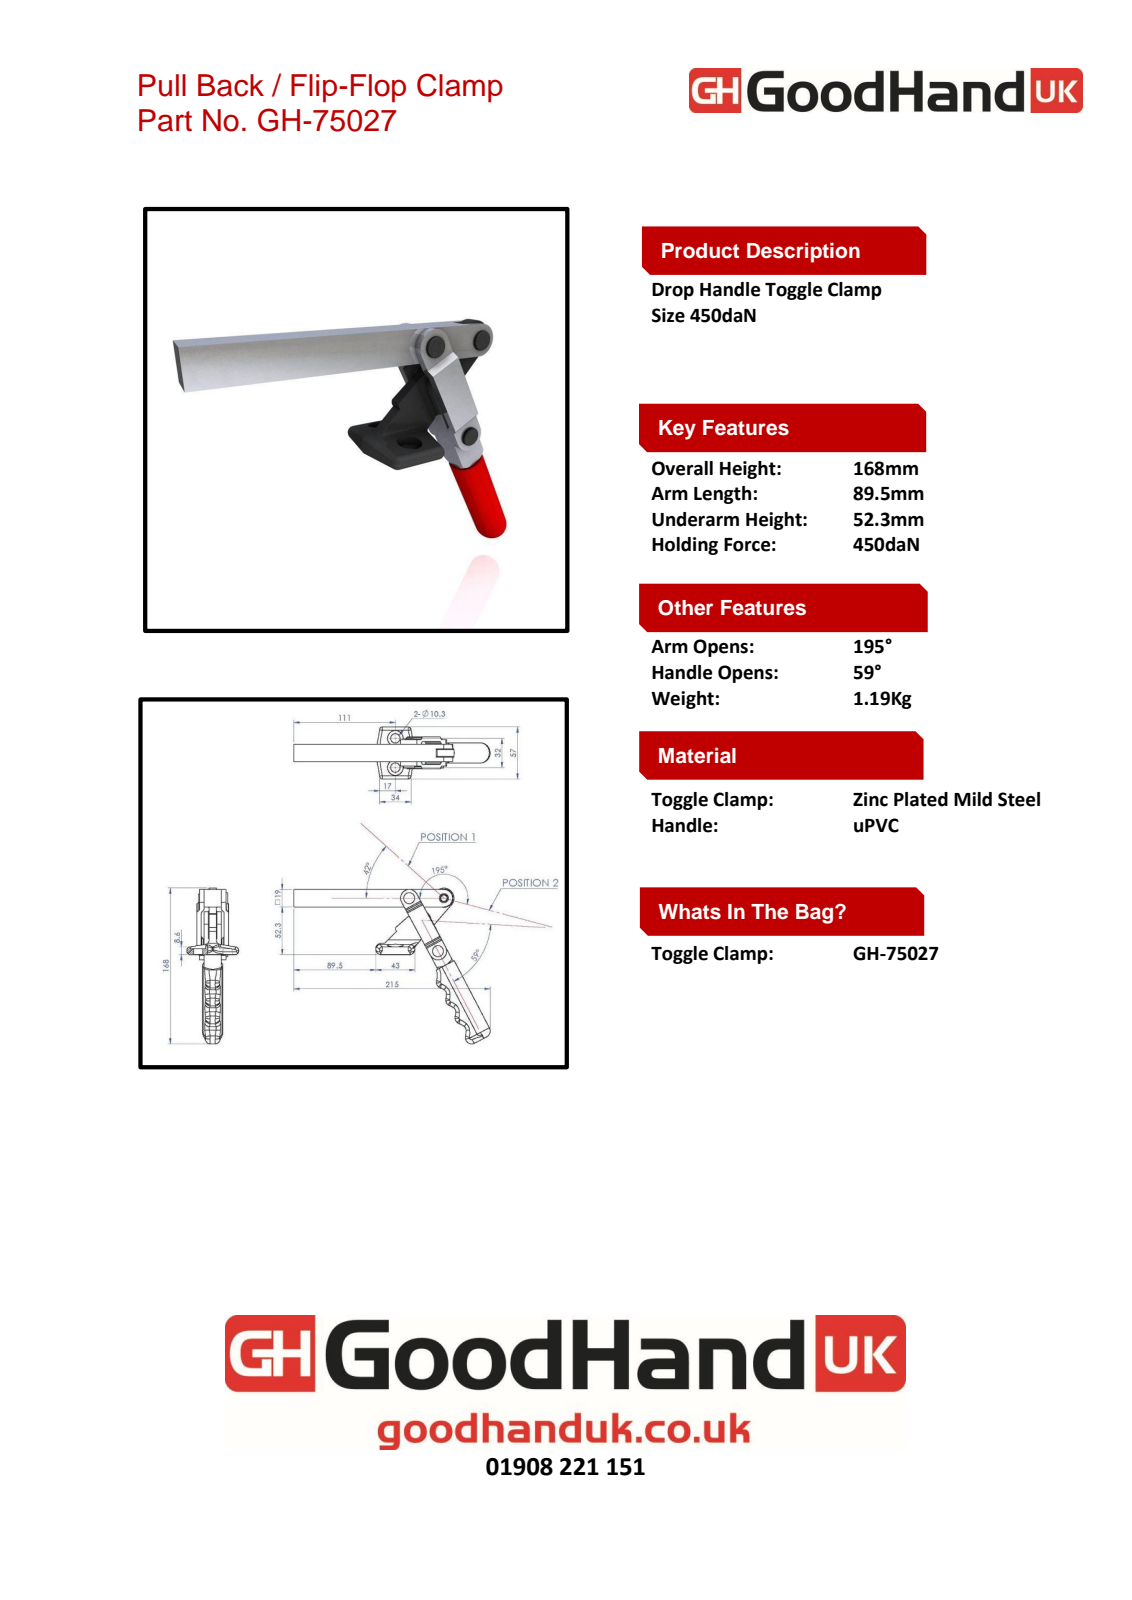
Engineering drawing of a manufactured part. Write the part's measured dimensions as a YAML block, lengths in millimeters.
part_name: "Group3^GH-75027(簡化); GH-75027(簡化); Group2^GH-75027(簡化); 27502713-2^GH-75027(簡化) (+1 more)"
step_written_by: "SolidWorks 2016 (AUTOMOTIVE_DESIGN)"
units: millimeters
bodies: {solids: 4, faces: 265, planar: 72, cylindrical: 116, other: 77}
overall_size: [214.63, 170.5, 57]
volume: 166800
surface_area: 48815
round_holes:
  - {diameter: 6, count: 4}
  - {diameter: 10.3, count: 2}
  - {diameter: 17.1, count: 2}
round_bosses_or_shafts:
  - {diameter: 20, count: 2}
  - {diameter: 10, count: 2}
  - {diameter: 7, count: 2}
partial_cylinders:
  - {radius: 2, count: 16}
  - {radius: 3, count: 12}
  - {radius: 20, count: 7}
  - {radius: 5, count: 6}
  - {radius: 7, count: 4}
  - {radius: 9.5, count: 4}
  - {radius: 0.5, count: 3}
  - {radius: 4.31, count: 2}
face_to_face_distances: [19, 5, 4.9, 14.1, 3, 27, 22, 8, 8.45, 0.65]
hole_center_spacings: [27.87, 32, 34.16, 38, 38.14, 58.35, 65.99]
